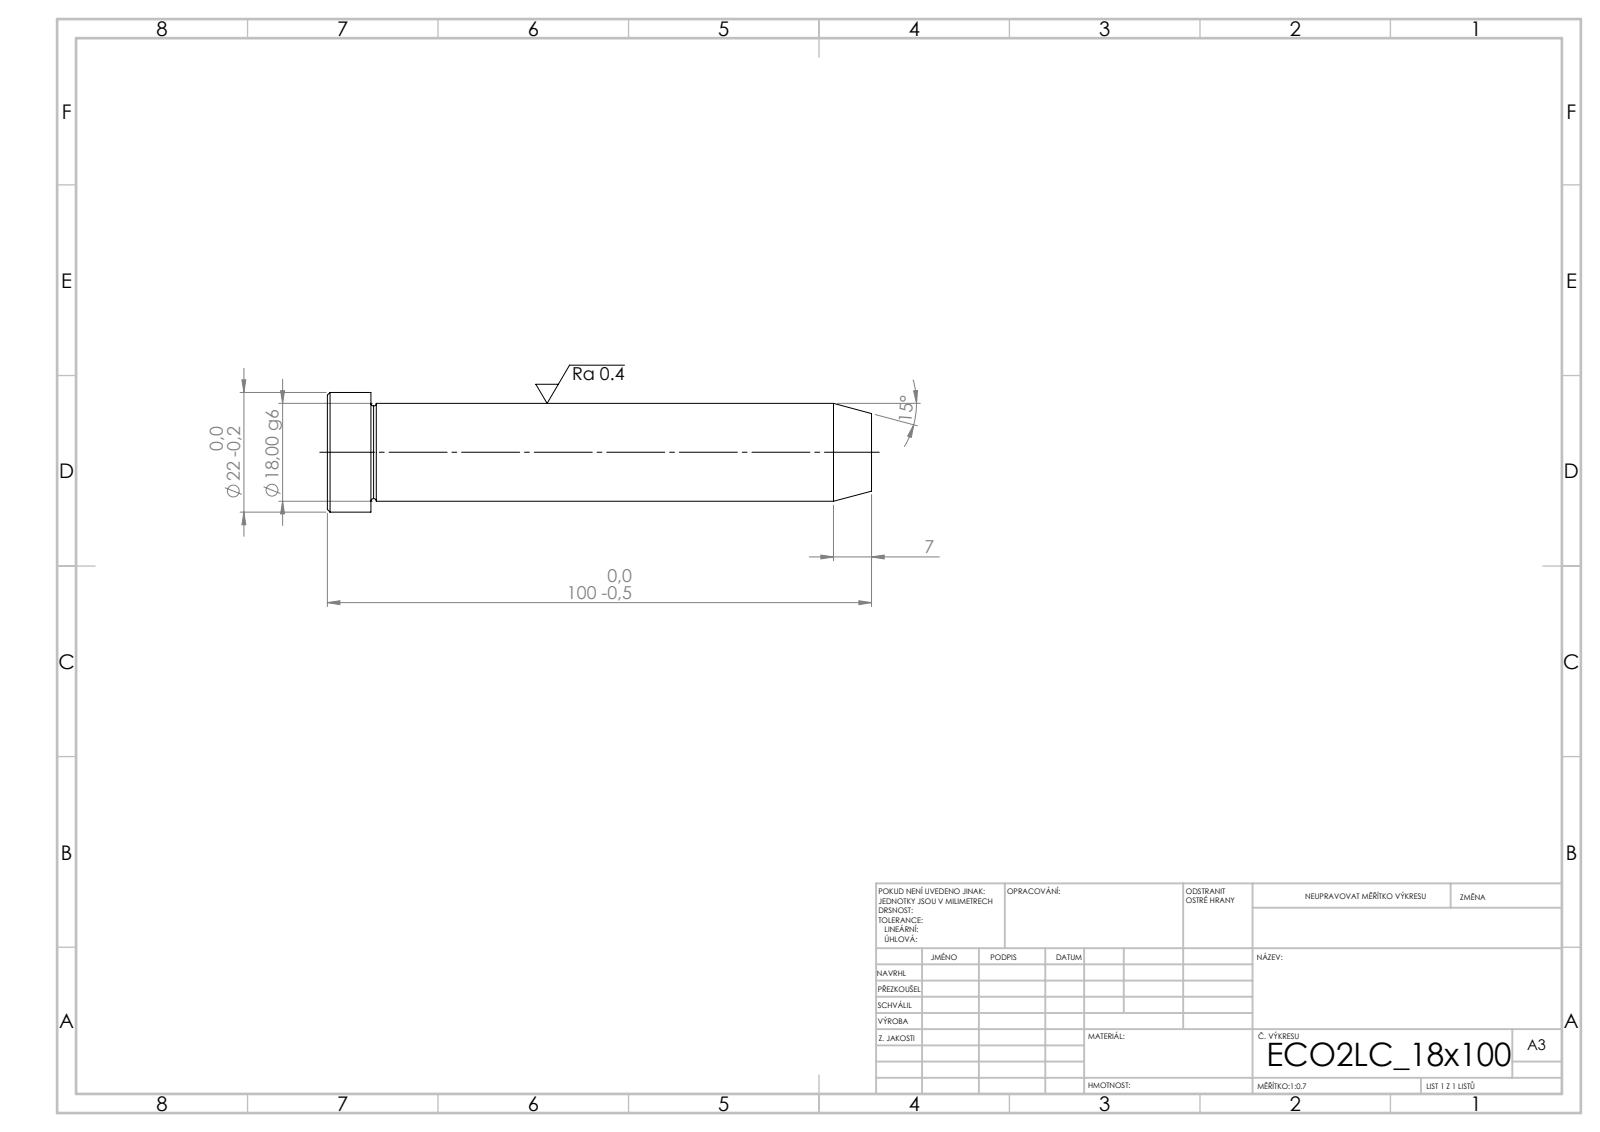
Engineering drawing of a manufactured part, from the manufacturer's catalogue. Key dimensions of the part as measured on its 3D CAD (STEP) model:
STEP written by: SolidWorks 2019 (CONFIG_CONTROL_DESIGN)
Units: millimetres
Bodies: 1 solid, 15 faces (3 planar, 4 cylindrical, 8 other)
Overall size (bounding box): 100 × 22 × 22
Volume: 26 077 mm³ · Surface area: 6 400 mm²
Round bosses / shafts (diameter × count): ⌀22 ×1, ⌀18 ×1
Main face-to-face distances: 100, 92, 8
